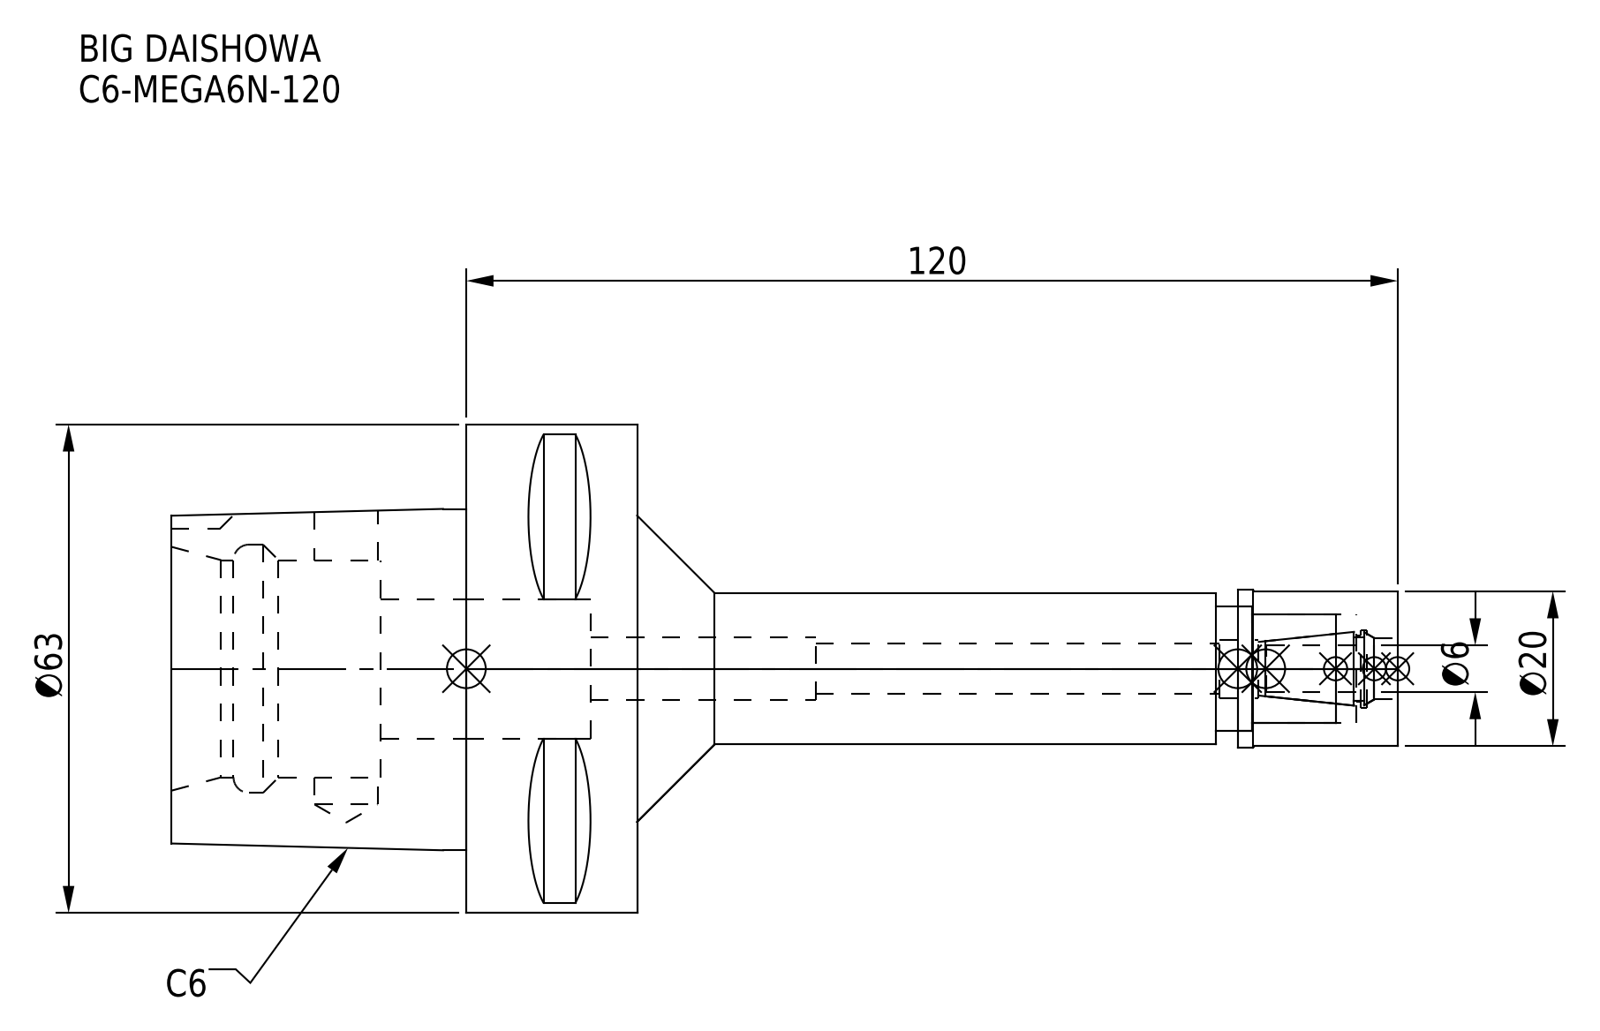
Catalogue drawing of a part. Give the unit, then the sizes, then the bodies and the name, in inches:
Units: inches
Overall size (bounding box): 6.22 × 2.48 × 2.48
Round holes (diameter × count): ⌀0.252 ×1, ⌀0.295 ×1, ⌀0.311 ×1, ⌀0.315 ×1, ⌀0.319 ×1, ⌀0.335 ×1, ⌀0.394 ×1, ⌀0.551 ×1, ⌀0.63 ×1, ⌀0.709 ×1, ⌀1.102 ×1, ⌀1.26 ×1
Round bosses / shafts (diameter × count): ⌀2.48 ×1, ⌀0.799 ×1, ⌀0.787 ×1, ⌀0.768 ×1
Partial cylindrical surfaces — rounded edges, fillets, slot ends (radius × count): R0.197 ×1
Main face-to-face distances: 0.866, 1.063, 2.362, 1.496, 1.299, 0.433, 3.858, 4.724, 5.157, 6.22
Volume: 7.656 in³ · Surface area: 46.42 in²
Bodies: 2 solids, 98 faces (39 planar, 41 cylindrical, 18 other)
Part name (STEP PRODUCT): C6-MEGA6N-120-060_ASM.stp; C6-MEGA6N-120_1.stp; C6-MEGA6N-120-060-FreeParts; DXF_TEMP_ASSY_ASM_4_ASM.stp (+3 more)
STEP written by: SolidWorks 2019 (CONFIG_CONTROL_DESIGN)
